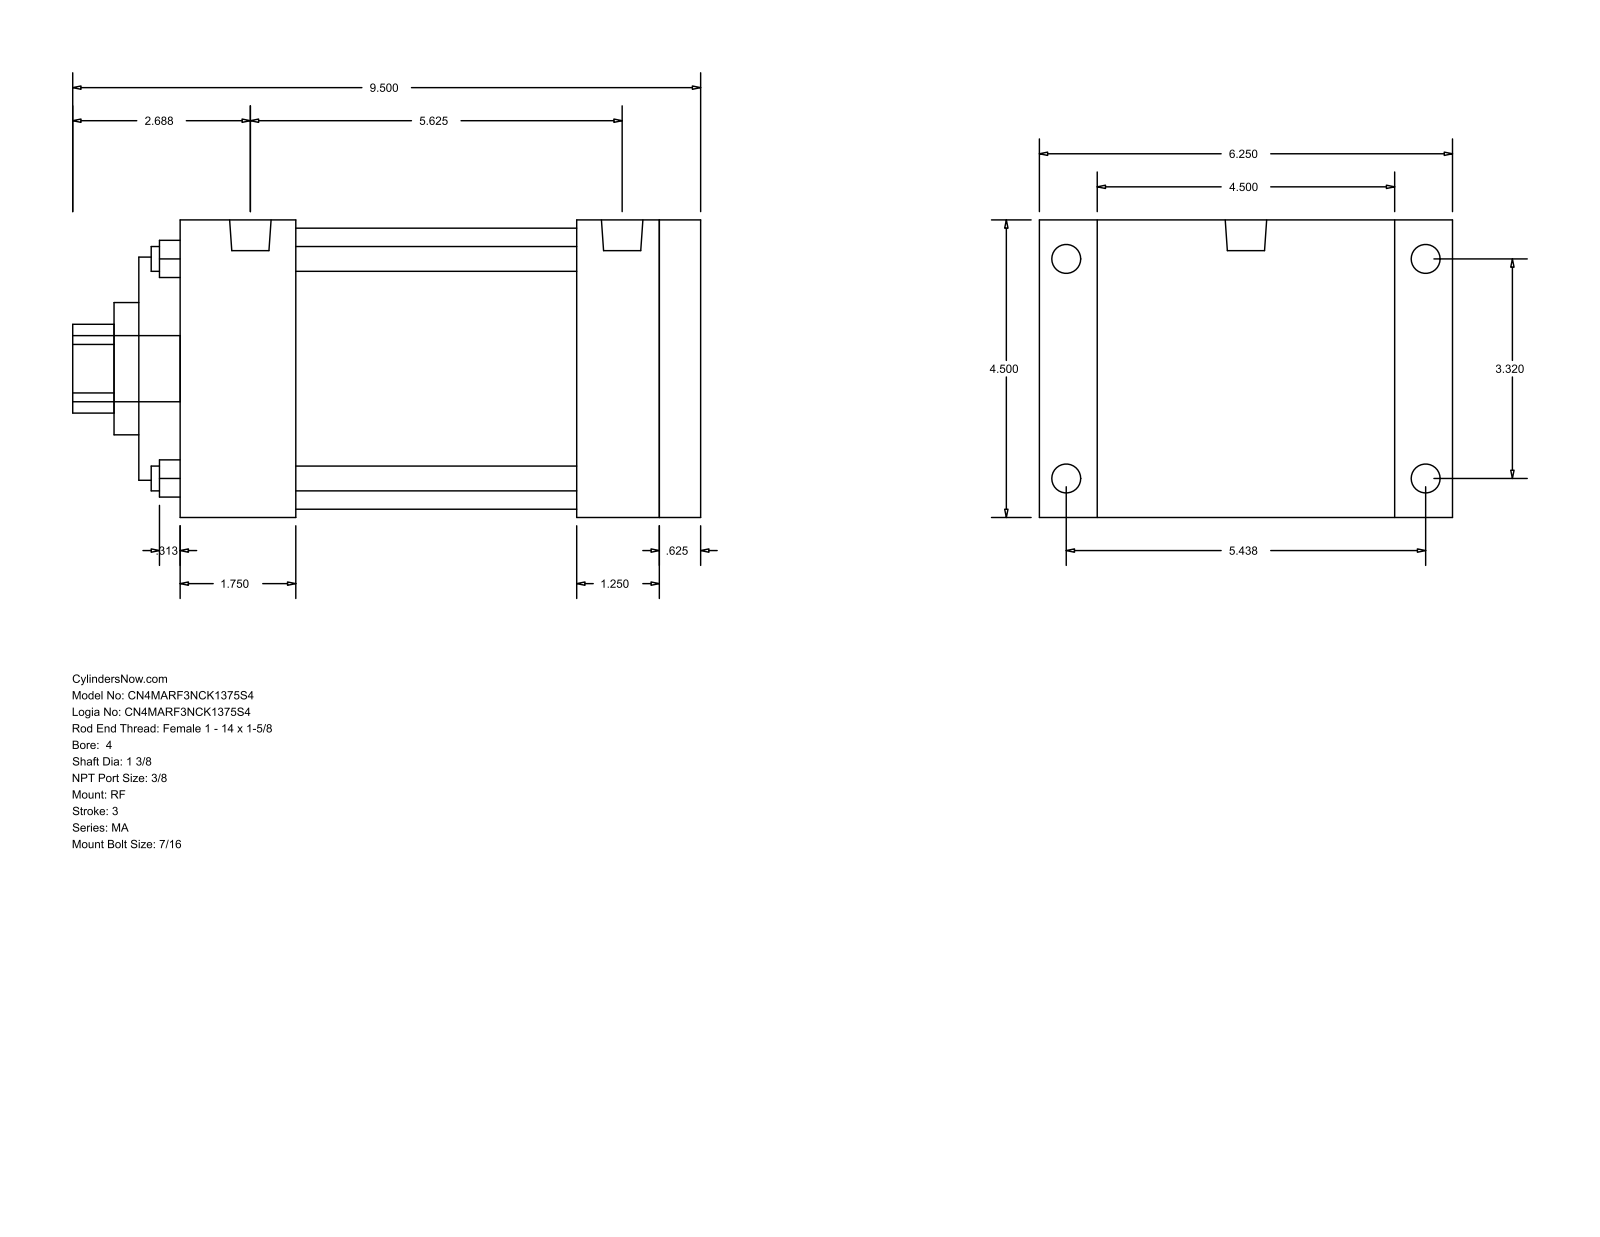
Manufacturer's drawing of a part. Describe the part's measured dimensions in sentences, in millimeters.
The part is named "MA_RF__0400_1.375". Its 3-D file was written by "GSSL Pune (CONFIG_CONTROL_DESIGN)". It is 0 solids with 94 faces: 65 planar, 29 cylindrical and 0 other. Overall it measures 241.3 by 158.75 by 114.3 millimeters. Round holes: 4 of diameter 9.53, 1 of diameter 34.92, 1 of diameter 50.8, 1 of diameter 85.72, 1 of diameter 107.95. Round bosses or shafts: 8 of diameter 11.11, 2 of diameter 15.93, 1 of diameter 25.4. Partial cylindrical surfaces (rounded edges, fillets, slot ends): 1 of radius 17.06. The main face-to-face distances are 114.3, 200.03, 15.87, 184.16, 215.9, 22.23, 136.53, 168.28, 152.41, 31.75. The hole center spacings are 59.62, 84.32, 119.25.
